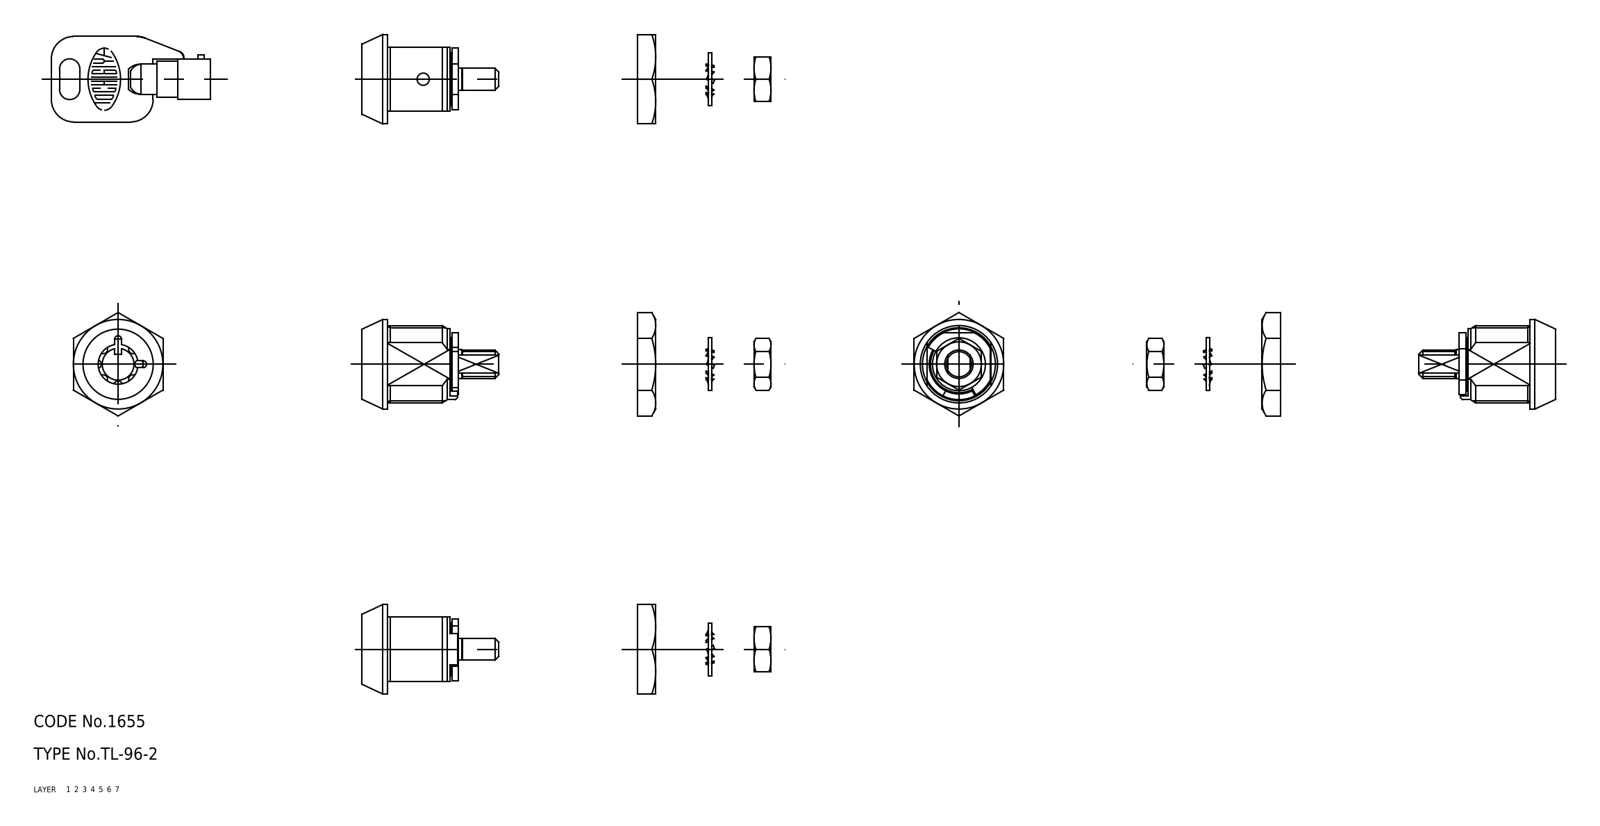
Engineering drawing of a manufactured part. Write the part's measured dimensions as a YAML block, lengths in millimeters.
part_name: "nut_B; nut_A; lock; key (+1 more)"
step_written_by: "CADfix (AUTOMOTIVE_DESIGN)"
units: millimeters
bodies: {solids: 4, faces: 146, planar: 0, cylindrical: 0, other: 146}
overall_size: [117.09, 25.4, 22]
volume: 8815
surface_area: 6322
